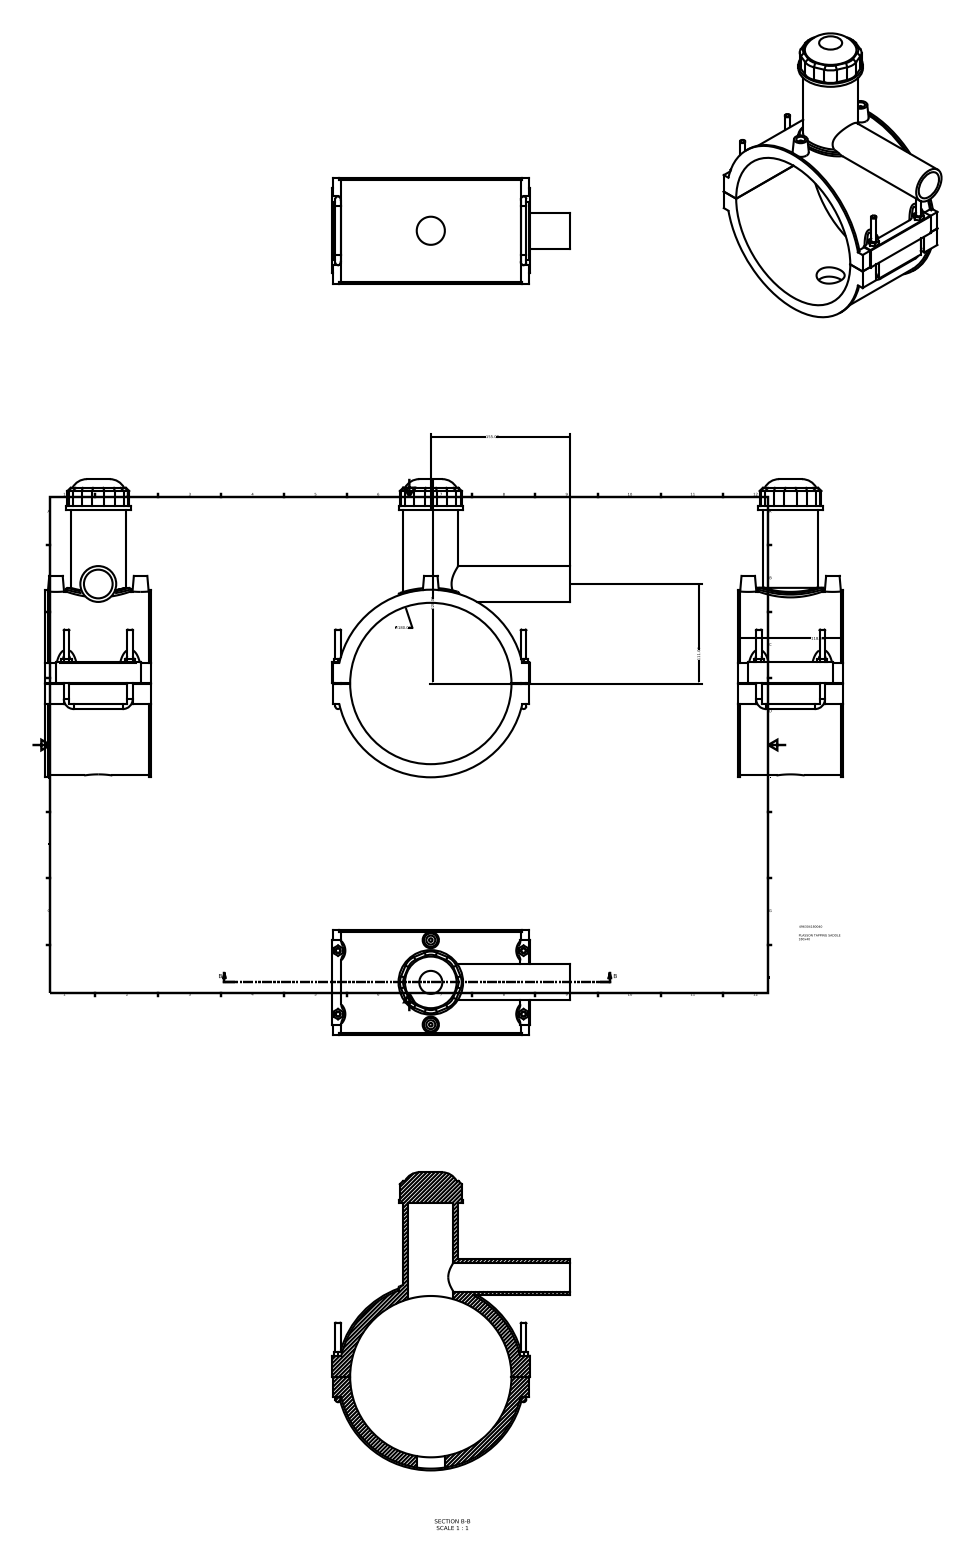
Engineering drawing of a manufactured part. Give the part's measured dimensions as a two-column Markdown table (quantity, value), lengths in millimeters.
| quantity | value |
| --- | --- |
| part name | 496304180040 |
| STEP written by | Autodesk Inventor 2015 (AUTOMOTIVE_DESIGN) |
| units | millimeters |
| bodies | 1 solid, 181 faces (110 planar, 47 cylindrical, 24 other) |
| overall size | 332.65 × 265.5 × 118 |
| volume | 1 221 000 mm³ |
| surface area | 257 782 mm² |
| round holes (diameter × count) | 10 × 2, 31.36 × 1, 32 × 1, 50.4 × 1, 180 × 1 |
| round bosses / shafts (diameter × count) | 6 × 6, 4 × 2, 209.3 × 1, 205.2 × 1, 72 × 1, 61.2 × 1, 40 × 1 |
| partial cylindrical surfaces (radius × count) | 18 × 8, 3 × 4, 7.5 × 4, 0.5 × 1, 106.7 × 1 |
| main face-to-face distances | 118, 1, 220, 193.55, 193.45, 219, 22.45, 22.55, 2.36, 115.64 |
| hole center spacings | 47.2, 94.4 |
